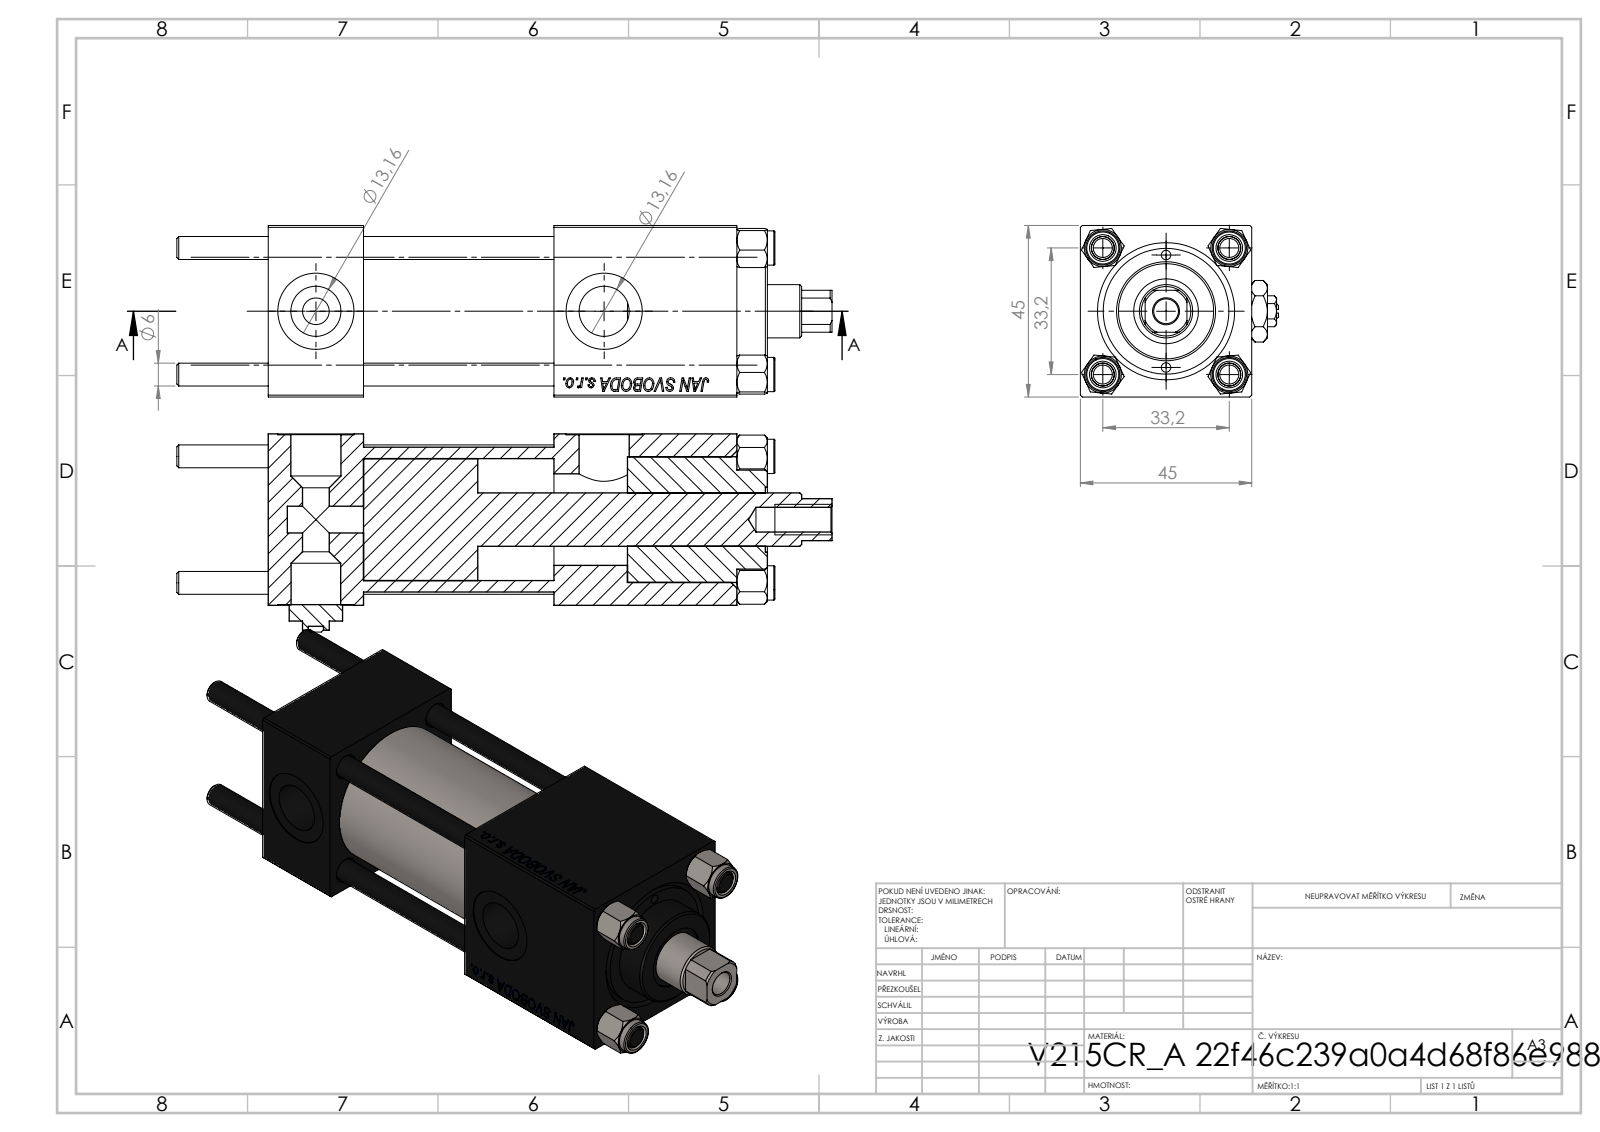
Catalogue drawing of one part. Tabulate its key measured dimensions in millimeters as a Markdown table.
| quantity | value |
| --- | --- |
| part name | V215CR_BODY_A; Zatka_pro_OIL_PORT; NUT_M5; V215CR_VCP (+2 more) |
| STEP written by | SolidWorks 2019 (CONFIG_CONTROL_DESIGN) |
| units | millimeters |
| bodies | 12 solids, 1190 faces (542 planar, 90 cylindrical, 558 other) |
| overall size | 172 × 52 × 45 |
| volume | 197 045 mm³ |
| surface area | 74 025 mm² |
| round holes (diameter × count) | 6 × 4, 2.5 × 2, 7 × 2, 13.16 × 2, 20 × 2, 6.5 × 1, 13 × 1, 14 × 1, 17 × 1, 24 × 1, 32 × 1, 33 × 1 |
| round bosses / shafts (diameter × count) | 9 × 4, 38 × 1, 26 × 1 |
| partial cylindrical surfaces (radius × count) | 6.5 × 1 |
| main face-to-face distances | 45, 25, 123, 98, 50, 75, 48, 94.3, 69.3, 19.3 |
| hole center spacings | 16.7, 23.48, 33.2, 35.47, 14.75, 46.95, 29.5, 75.66 |
